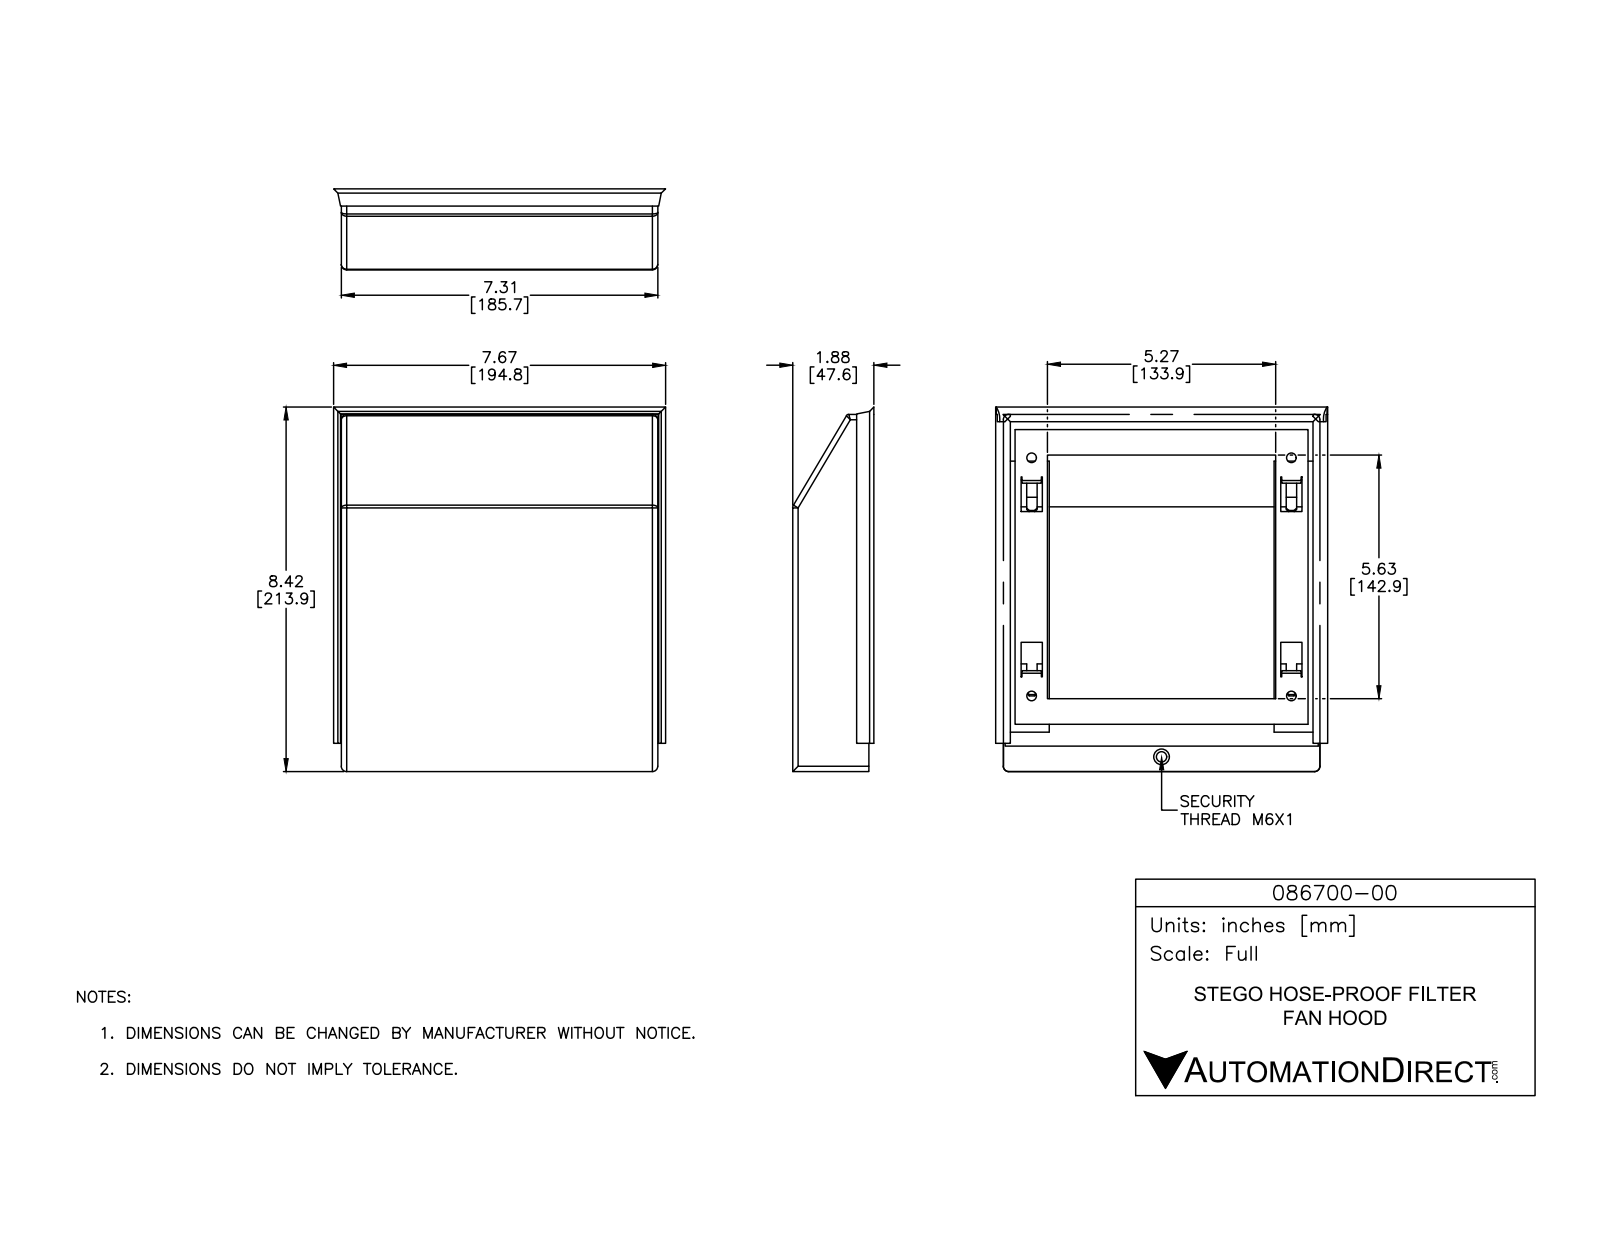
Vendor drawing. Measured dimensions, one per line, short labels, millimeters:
name: 08670.0-00_2; 08670.0-00_3; 086700-00; 08670.0-00_1
written by: SolidWorks 2017 (AUTOMOTIVE_DESIGN)
unit: mm
bodies: 6 solids, 232 faces (187 planar, 41 cylindrical, 4 other)
size: 213.9 × 194.8 × 47.6
volume: 127 400 mm³; area: 214 800 mm²
holes: 4× ⌀5.6, 1× ⌀6, 1× ⌀9.1
bosses: 1× ⌀10.2
rounds: 9× R3.2, 5× R1.6, 4× R1.5, 3× R12.7
face distances: 1, 1, 184.7, 1.9, 183.7, 41.8, 42.8, 2, 39.9, 40.9
hole spacings: 139.7, 152.4, 206.7, 84.1, 84.2, 191.3, 191.3
